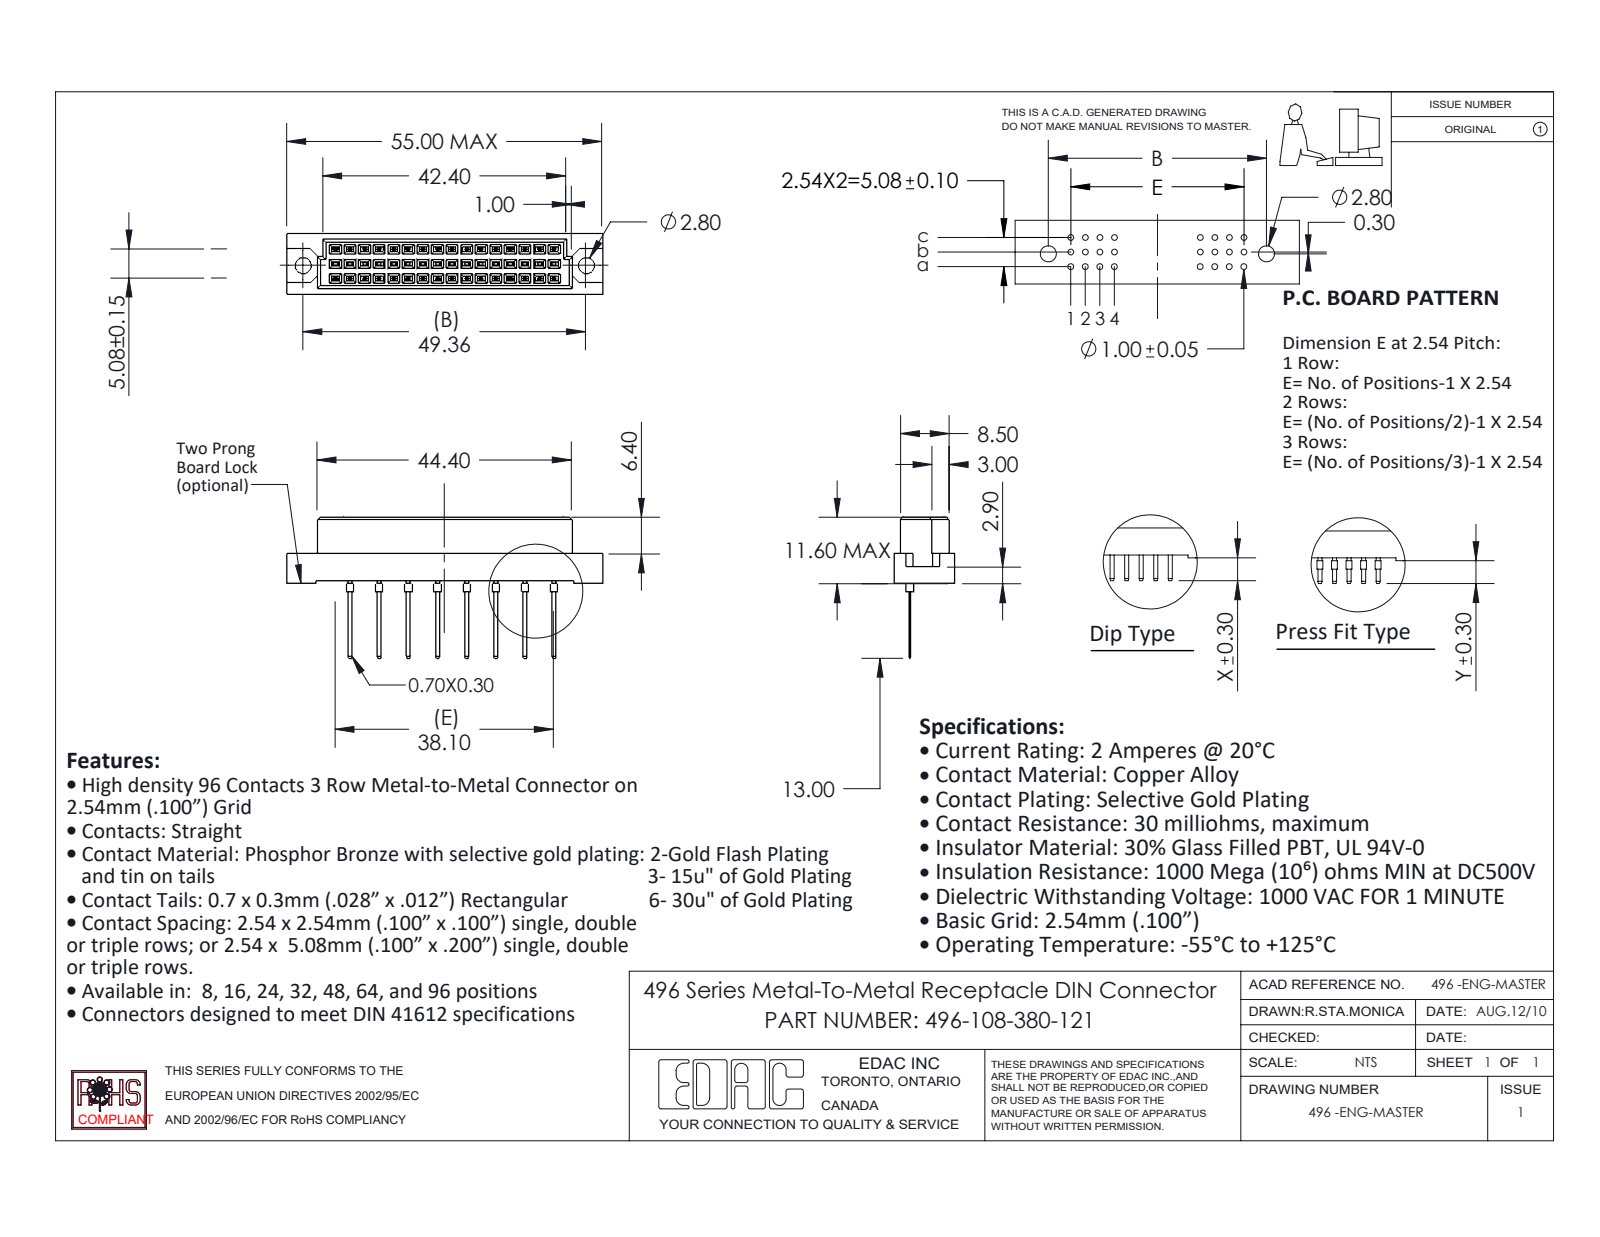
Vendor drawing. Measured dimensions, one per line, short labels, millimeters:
name: 496-290_80; 496-108-380-121; 496 Part_48
written by: SolidWorks 2020 (CONFIG_CONTROL_DESIGN)
unit: mm
bodies: 9 solids, 810 faces (790 planar, 20 cylindrical, 0 other)
size: 55 × 24.6 × 10.6
volume: 4 626 mm³; area: 4 524 mm²
holes: 2× ⌀2.8
bosses: 8× ⌀1
face distances: 2.54, 5.08, 1.05, 9.55, 0.81, 10.6, 3.35, 1.73, 8.5, 0.56
hole spacings: 49.36
